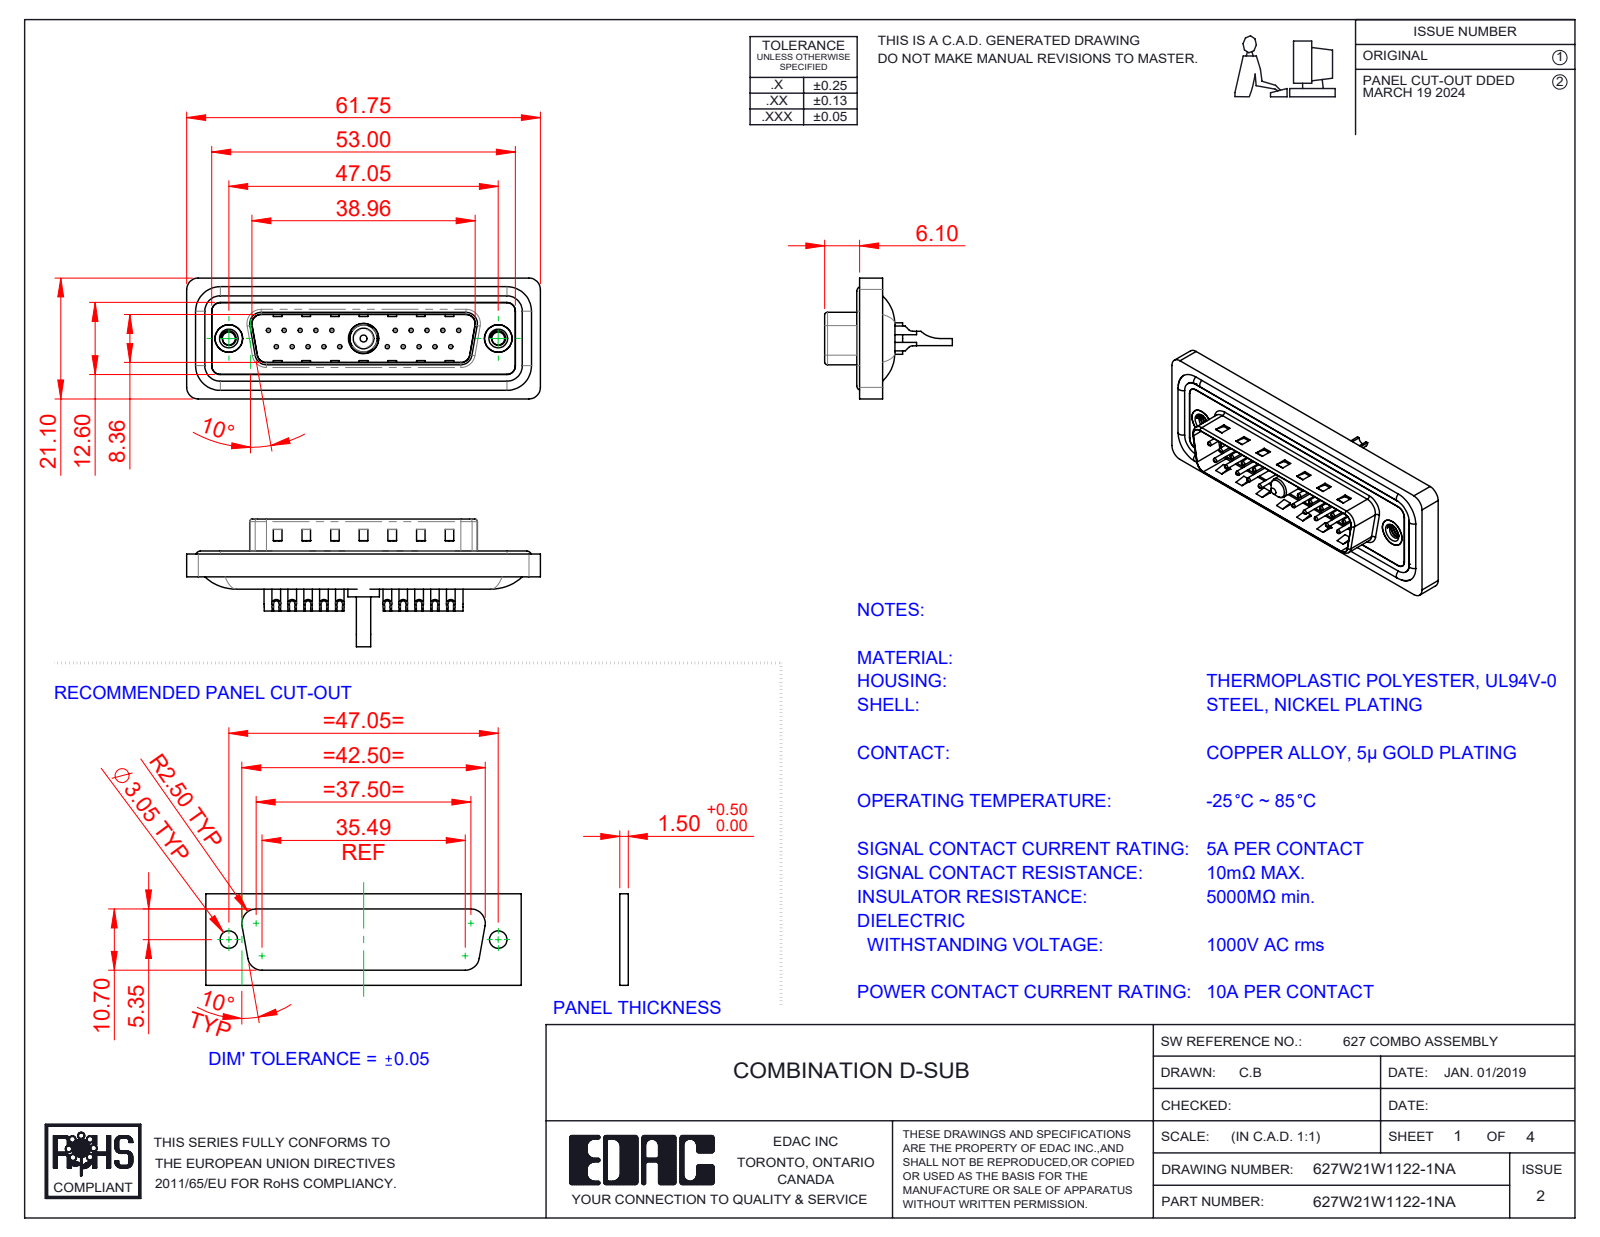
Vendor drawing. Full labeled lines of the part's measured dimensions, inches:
Part name (STEP PRODUCT): 627Combo Shell Front_25 Contacts; 627Combo Waterproof Housing_25 Contacts; 627Combo Contact Row 2_22; 627Combo Housing_21W1 (+5 more)
STEP written by: SolidWorks 2023 (CONFIG_CONTROL_DESIGN)
Units: inches
Bodies: 29 solids, 1265 faces (401 planar, 532 cylindrical, 332 other)
Overall size (bounding box): 2.431 × 0.878 × 0.831
Volume: 0.441 in³ · Surface area: 18.84 in²
Round holes (diameter × count): ⌀0.03 ×20, ⌀0.039 ×20, ⌀0.063 ×20, ⌀0.079 ×20, ⌀0.089 ×2, ⌀0.157 ×2, ⌀0.189 ×2, ⌀0.197 ×2, ⌀0.067 ×1, ⌀0.191 ×1, ⌀0.209 ×1
Round bosses / shafts (diameter × count): ⌀0.059 ×20, ⌀0.063 ×4, ⌀0.193 ×2, ⌀0.217 ×1, ⌀0.205 ×1, ⌀0.187 ×1, ⌀0.148 ×1, ⌀0.142 ×1
Partial cylindrical surfaces — rounded edges, fillets, slot ends (radius × count): R0.059 ×22, R0.079 ×18, R0.02 ×8, R0.063 ×8, R0.039 ×6, R0.01 ×4, R0.024 ×4, R0.026 ×4
Main face-to-face distances: 0.016, 0.059, 0.043, 0.063, 0.02, 0.122, 0.114, 0.161, 0.032, 0.377
Hole centre spacings: 0.124, 0.109, 0.218, 0.327, 0.198, 0.763, 0.826, 0.872
